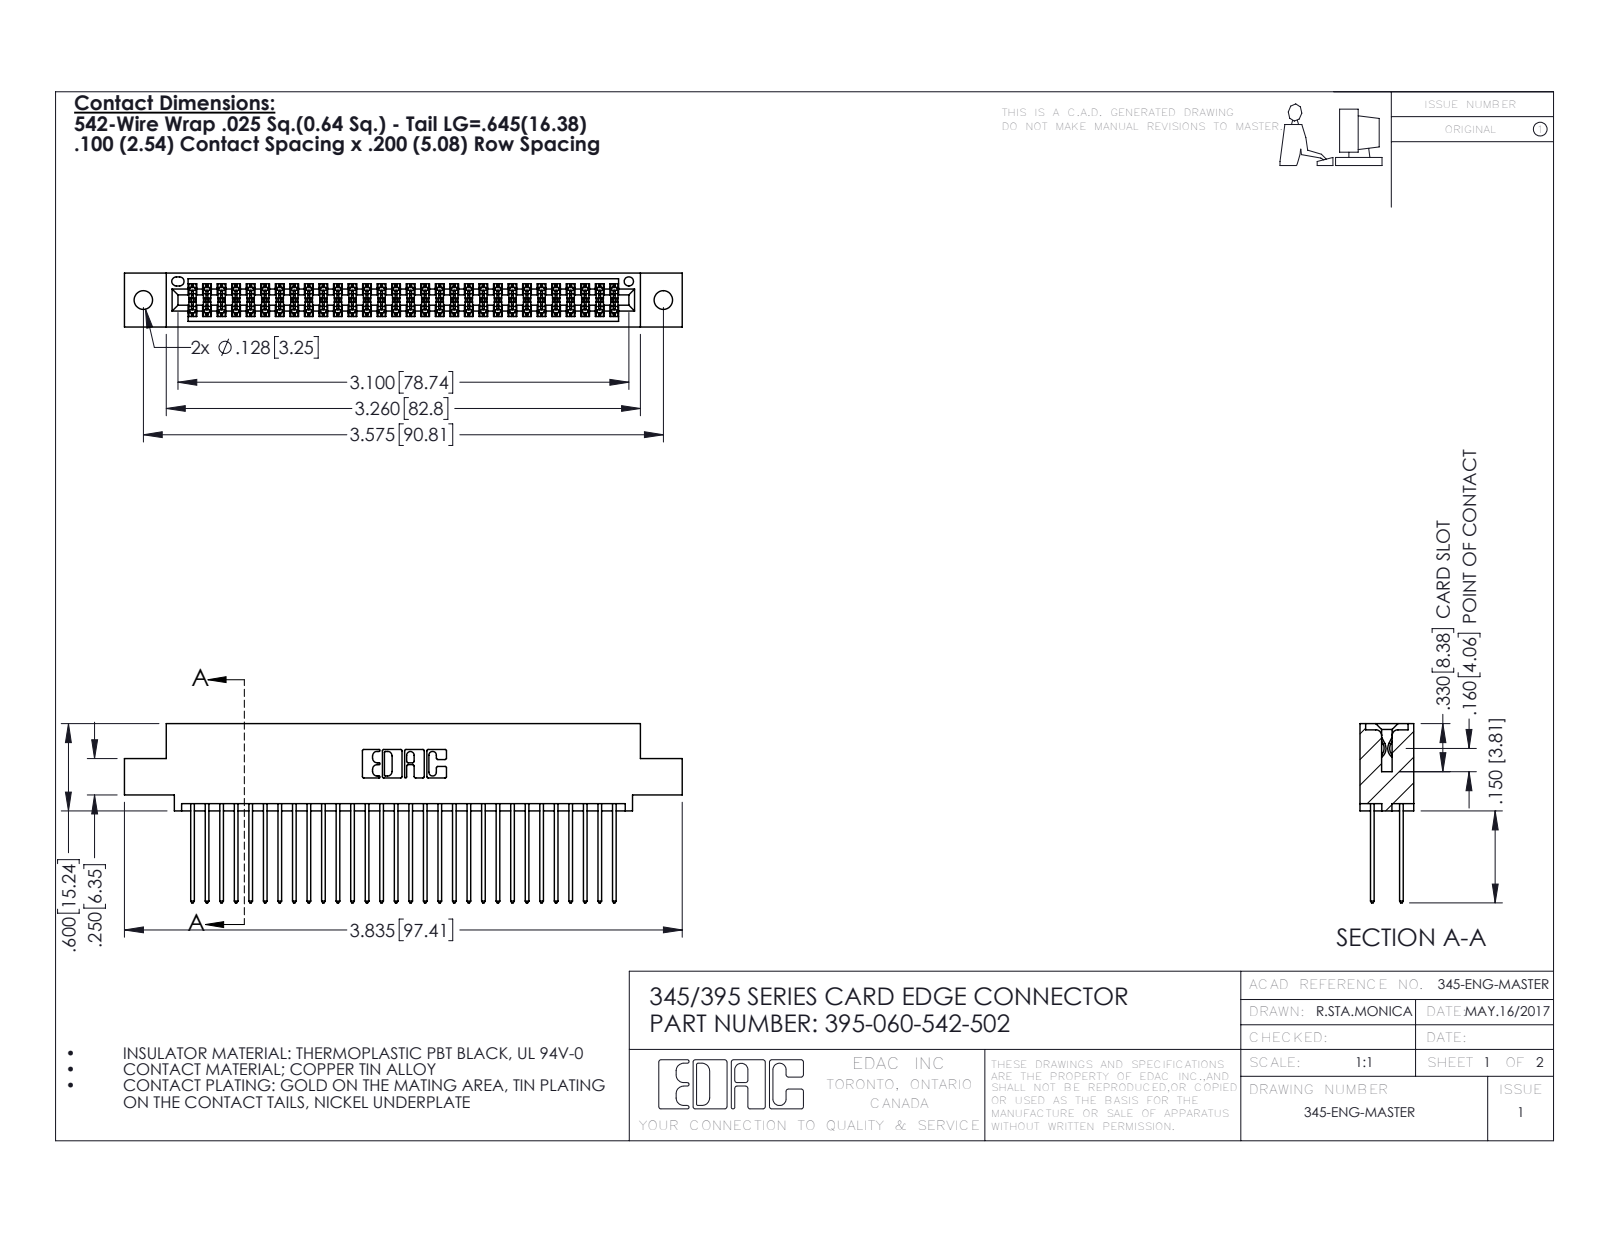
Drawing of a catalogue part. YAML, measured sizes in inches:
part_name: "345 Part_0.110 Offset - 0.128 Dia; 395-060-542-502; 345-292-001_345-293-142"
step_written_by: "SolidWorks 2016 (CONFIG_CONTROL_DESIGN)"
units: inches
bodies: {solids: 61, faces: 3130, planar: 2064, cylindrical: 1066, other: 0}
overall_size: [3.835, 1.232, 0.37]
volume: 0.581
surface_area: 23.2
round_holes:
  - {diameter: 0.128, count: 2}
  - {diameter: 0.064, count: 1}
partial_cylinders:
  - {radius: 0.006, count: 90}
  - {radius: 0.01, count: 60}
  - {radius: 0.01, count: 22}
  - {radius: 0.007, count: 6}
  - {radius: 0.031, count: 6}
  - {radius: 0.026, count: 3}
  - {radius: 0.014, count: 2}
  - {radius: 0.019, count: 2}
face_to_face_distances: [0.298, 0.072, 0.2, 0.098, 0.272, 0.025, 0.37, 0.225, 0.175, 0.149]
hole_center_spacings: [0.27, 3.34, 3.575]
